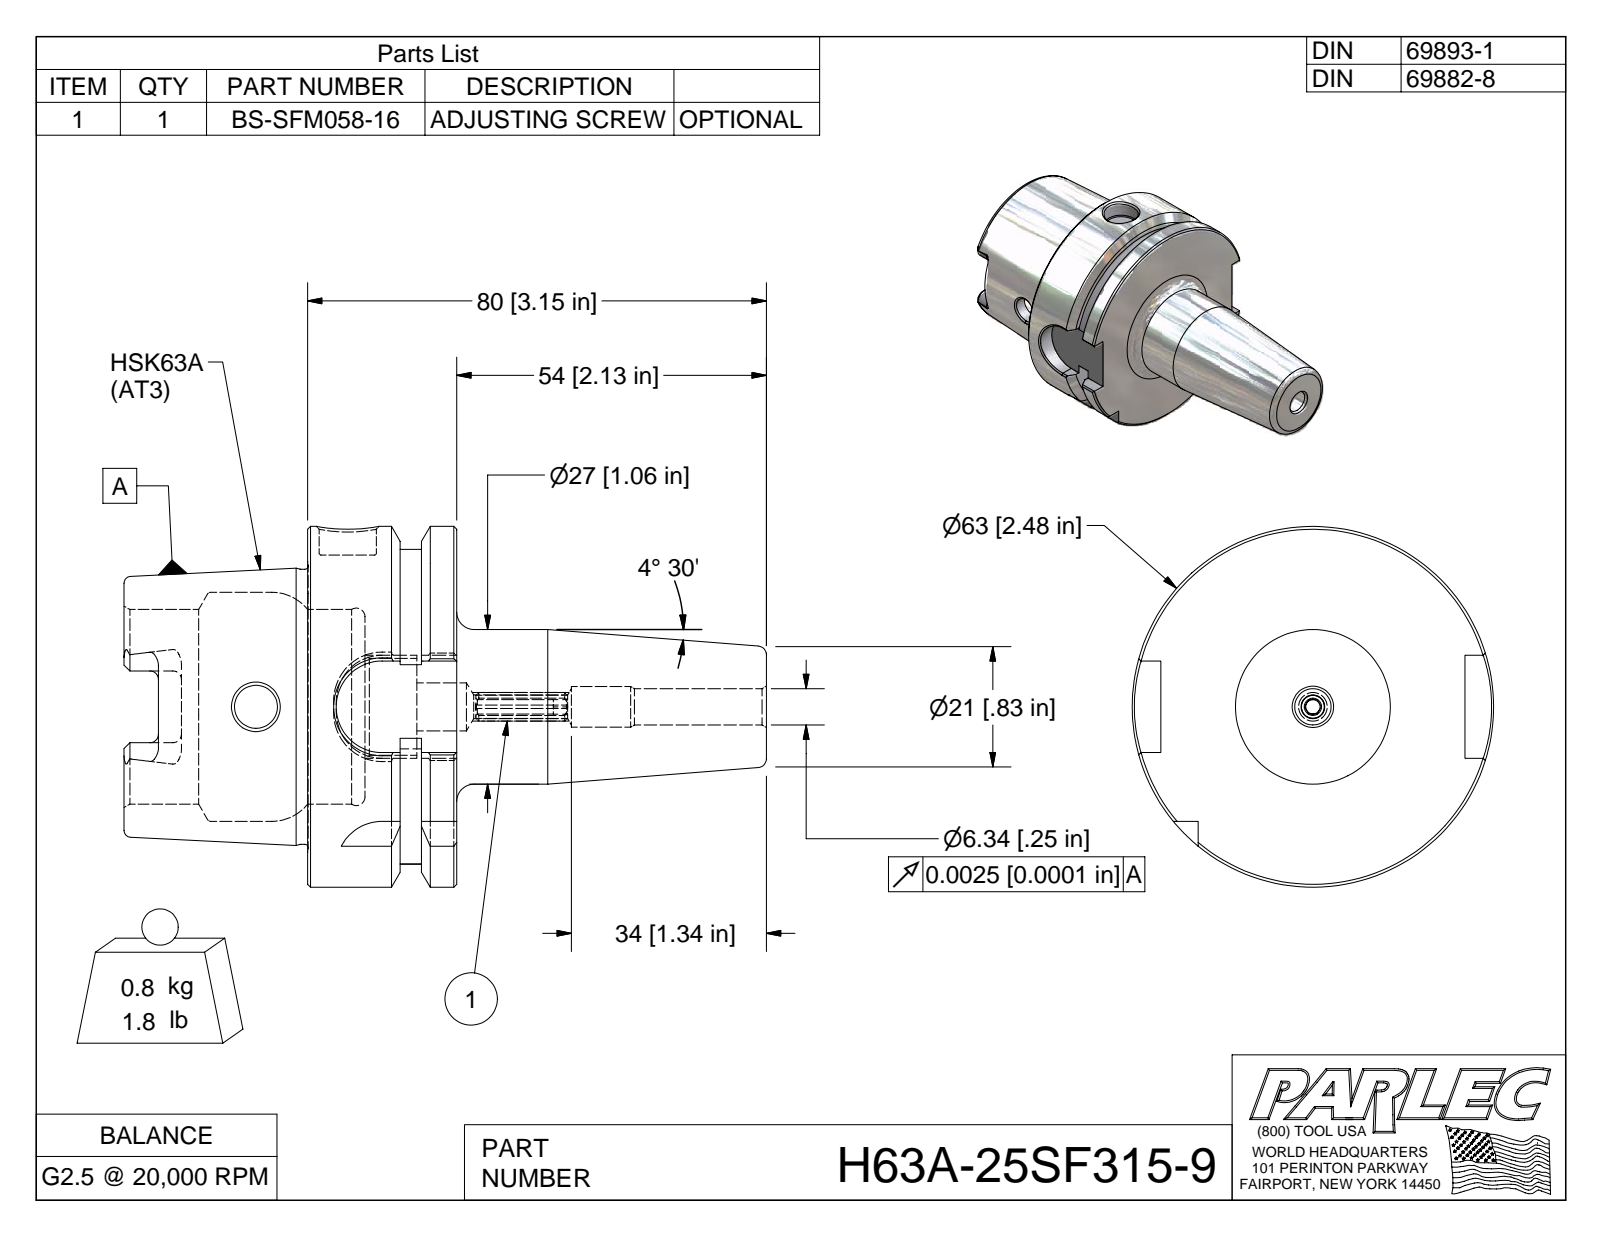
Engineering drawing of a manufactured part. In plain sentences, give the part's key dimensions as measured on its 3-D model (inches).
The part is named "H63A-25SF315-9; H63A-25SF315-9-1; BS-SFM058-16". Its 3-D file was written by "Autodesk Inventor 2009 (AUTOMOTIVE_DESIGN)". It is 2 solids with 157 faces: 58 planar, 35 cylindrical and 64 other. Overall it measures 4.409 by 2.48 by 2.48 inches. Its volume is 6.526 cubic inches and its surface area 42.78 square inches. Round holes: 1 of diameter 0.25, 1 of diameter 0.28, 1 of diameter 0.295, 1 of diameter 0.394, 1 of diameter 0.666, 1 of diameter 1.339, 1 of diameter 1.575. Round bosses or shafts: 1 of diameter 2.48, 1 of diameter 1.891, 1 of diameter 1.063. Partial cylindrical surfaces (rounded edges, fillets, slot ends): 6 of radius 0.059, 4 of radius 0.113, 4 of radius 0.315, 1 of radius 0.098, 1 of radius 1.083. The main face-to-face distances are 1.024, 0.241, 0.389, 0.394, 0.63, 1.26, 1.654, 2.283, 1.894, 0.635.
